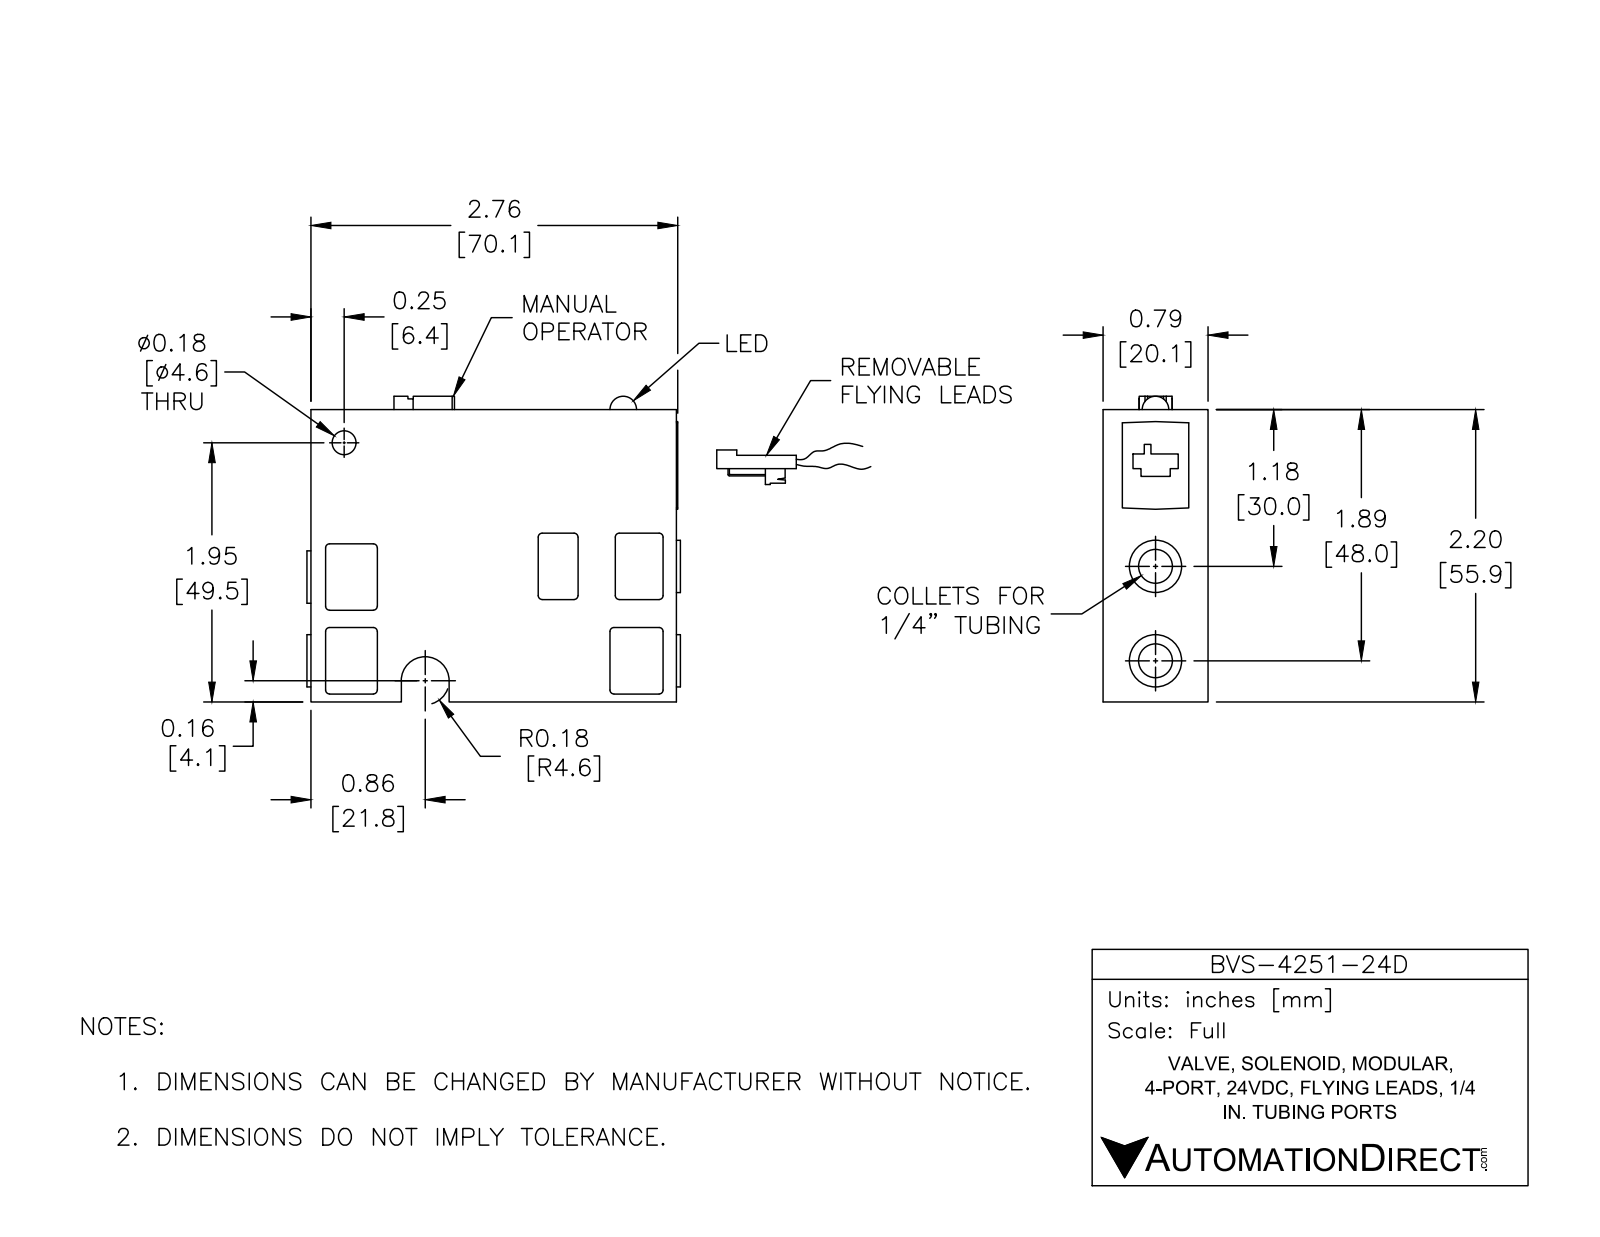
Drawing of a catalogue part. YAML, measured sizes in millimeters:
part_name: "BVS-4251-24D"
step_written_by: "SolidWorks 2016 (AUTOMOTIVE_DESIGN)"
units: millimeters
bodies: {solids: 1, faces: 173, planar: 85, cylindrical: 78, other: 10}
overall_size: [76.4, 58.4, 20.1]
volume: 71640
surface_area: 16180
round_holes:
  - {diameter: 6.5, count: 3}
  - {diameter: 2.5, count: 1}
  - {diameter: 4.6, count: 1}
round_bosses_or_shafts:
  - {diameter: 1.5, count: 6}
  - {diameter: 10, count: 3}
partial_cylinders:
  - {radius: 0.8, count: 20}
  - {radius: 0.5, count: 2}
  - {radius: 3.2, count: 1}
  - {radius: 4.6, count: 1}
face_to_face_distances: [20.1, 2.5, 55.9, 17.5, 69.9, 15, 12.7, 2.8, 67.3, 70.1]
hole_center_spacings: [2, 14, 16, 16, 18, 32]
